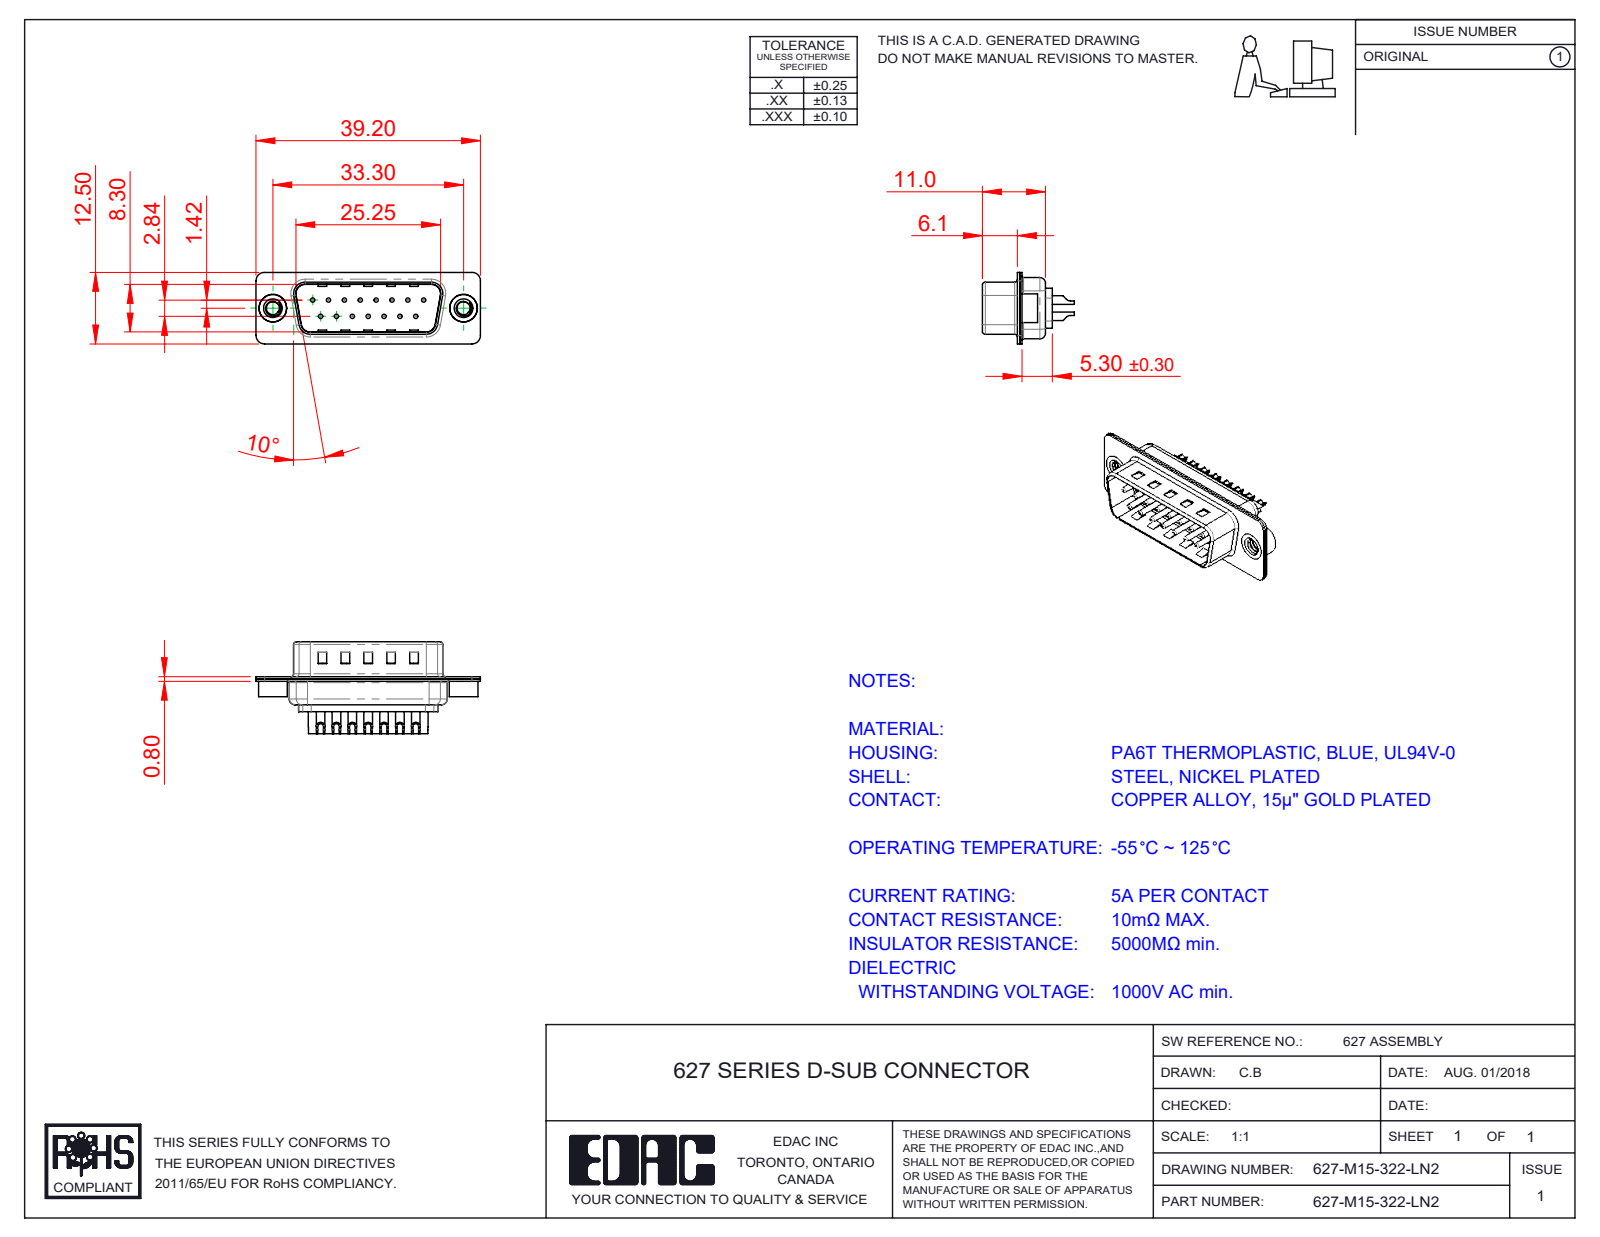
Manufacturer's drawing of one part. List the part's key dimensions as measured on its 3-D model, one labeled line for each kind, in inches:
Part name (STEP PRODUCT): 627M Shell Rear_15 Contacts; 627-M15-322-LN2; 627M Contact Row 1_22; 627M 4-40 Threaded Rivet (+3 more)
STEP written by: SolidWorks 2020 (CONFIG_CONTROL_DESIGN)
Units: inches
Bodies: 20 solids, 895 faces (274 planar, 373 cylindrical, 248 other)
Overall size (bounding box): 1.543 × 0.632 × 0.492
Volume: 0.115 in³ · Surface area: 7.671 in²
Round holes (diameter × count): ⌀0.03 ×15, ⌀0.039 ×15, ⌀0.063 ×15, ⌀0.079 ×15, ⌀0.089 ×2, ⌀0.157 ×2, ⌀0.189 ×2
Round bosses / shafts (diameter × count): ⌀0.059 ×15, ⌀0.197 ×2, ⌀0.193 ×2
Partial cylindrical surfaces — rounded edges, fillets, slot ends (radius × count): R0.059 ×16, R0.079 ×12, R0.02 ×8, R0.063 ×8, R0.039 ×6, R0.01 ×4, R0.024 ×4, R0.026 ×4
Main face-to-face distances: 0.016, 0.031, 0.374, 0.358, 0.343, 0.39, 0.047, 0.03, 0.014, 0.24
Hole centre spacings: 0.124, 0.109, 0.218, 0.327, 0.436, 0.198, 0.198, 0.294
